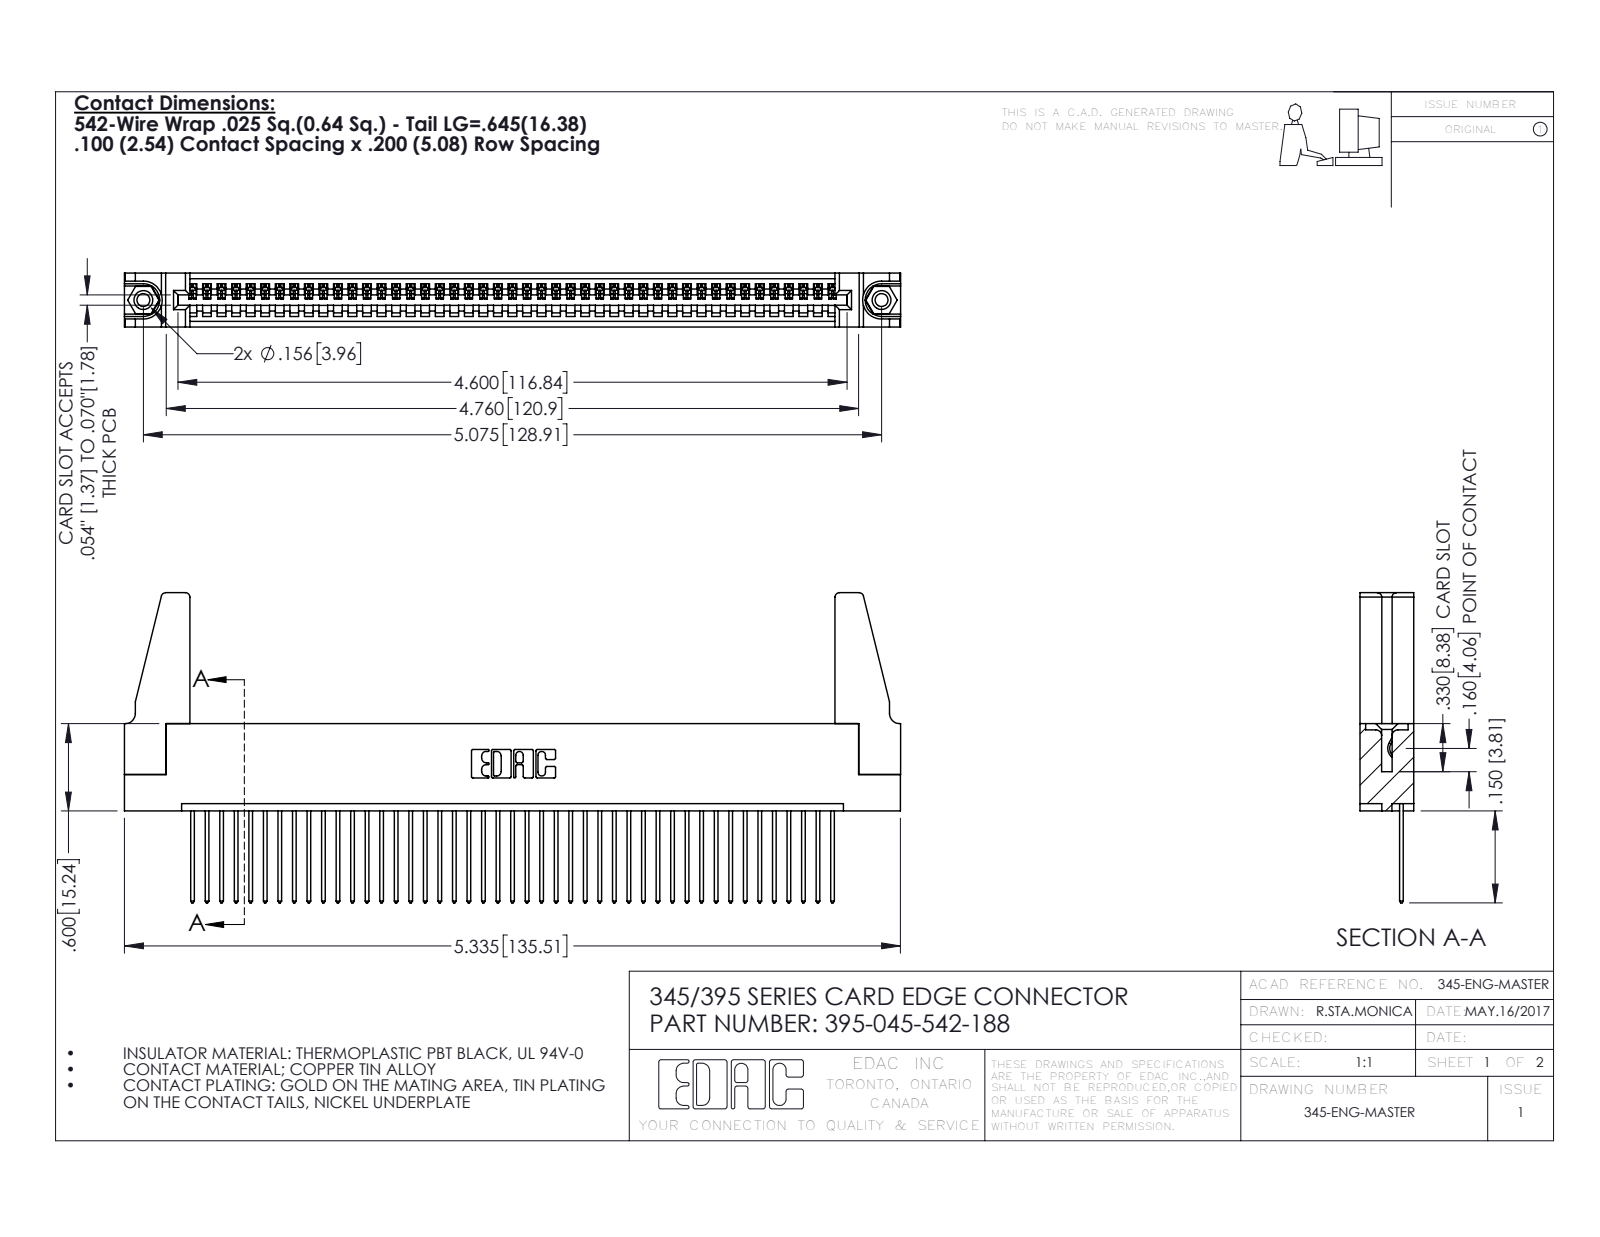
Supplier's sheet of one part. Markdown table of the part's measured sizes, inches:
| quantity | value |
| --- | --- |
| part name | 345 Part_Flush Mounting Lugs - 0.156 Dia-TH; 345-220-078_345-220-088; 345-250-001_345-250-001-102; 395-045-542-188 (+1 more) |
| STEP written by | SolidWorks 2016 (CONFIG_CONTROL_DESIGN) |
| units | inches |
| bodies | 50 solids, 2860 faces (1952 planar, 892 cylindrical, 16 other) |
| overall size | 5.336 × 2.132 × 0.37 |
| volume | 0.992 in³ |
| surface area | 32.67 in² |
| round holes (diameter × count) | 0.089 × 2, 0.125 × 2, 0.156 × 2, 0.064 × 1 |
| round bosses / shafts (diameter × count) | 0.155 × 2 |
| partial cylindrical surfaces (radius × count) | 0.006 × 90, 0.01 × 90, 0.01 × 22, 0.03 × 8, 0.007 × 6, 0.031 × 6, 0.026 × 3, 0.031 × 2 |
| main face-to-face distances | 0.072, 0.298, 0.37, 0.098, 0.272, 0.025, 0.2, 0.225, 0.149, 0.072 |
| hole center spacings | 0.27, 4.839, 5.075 |
